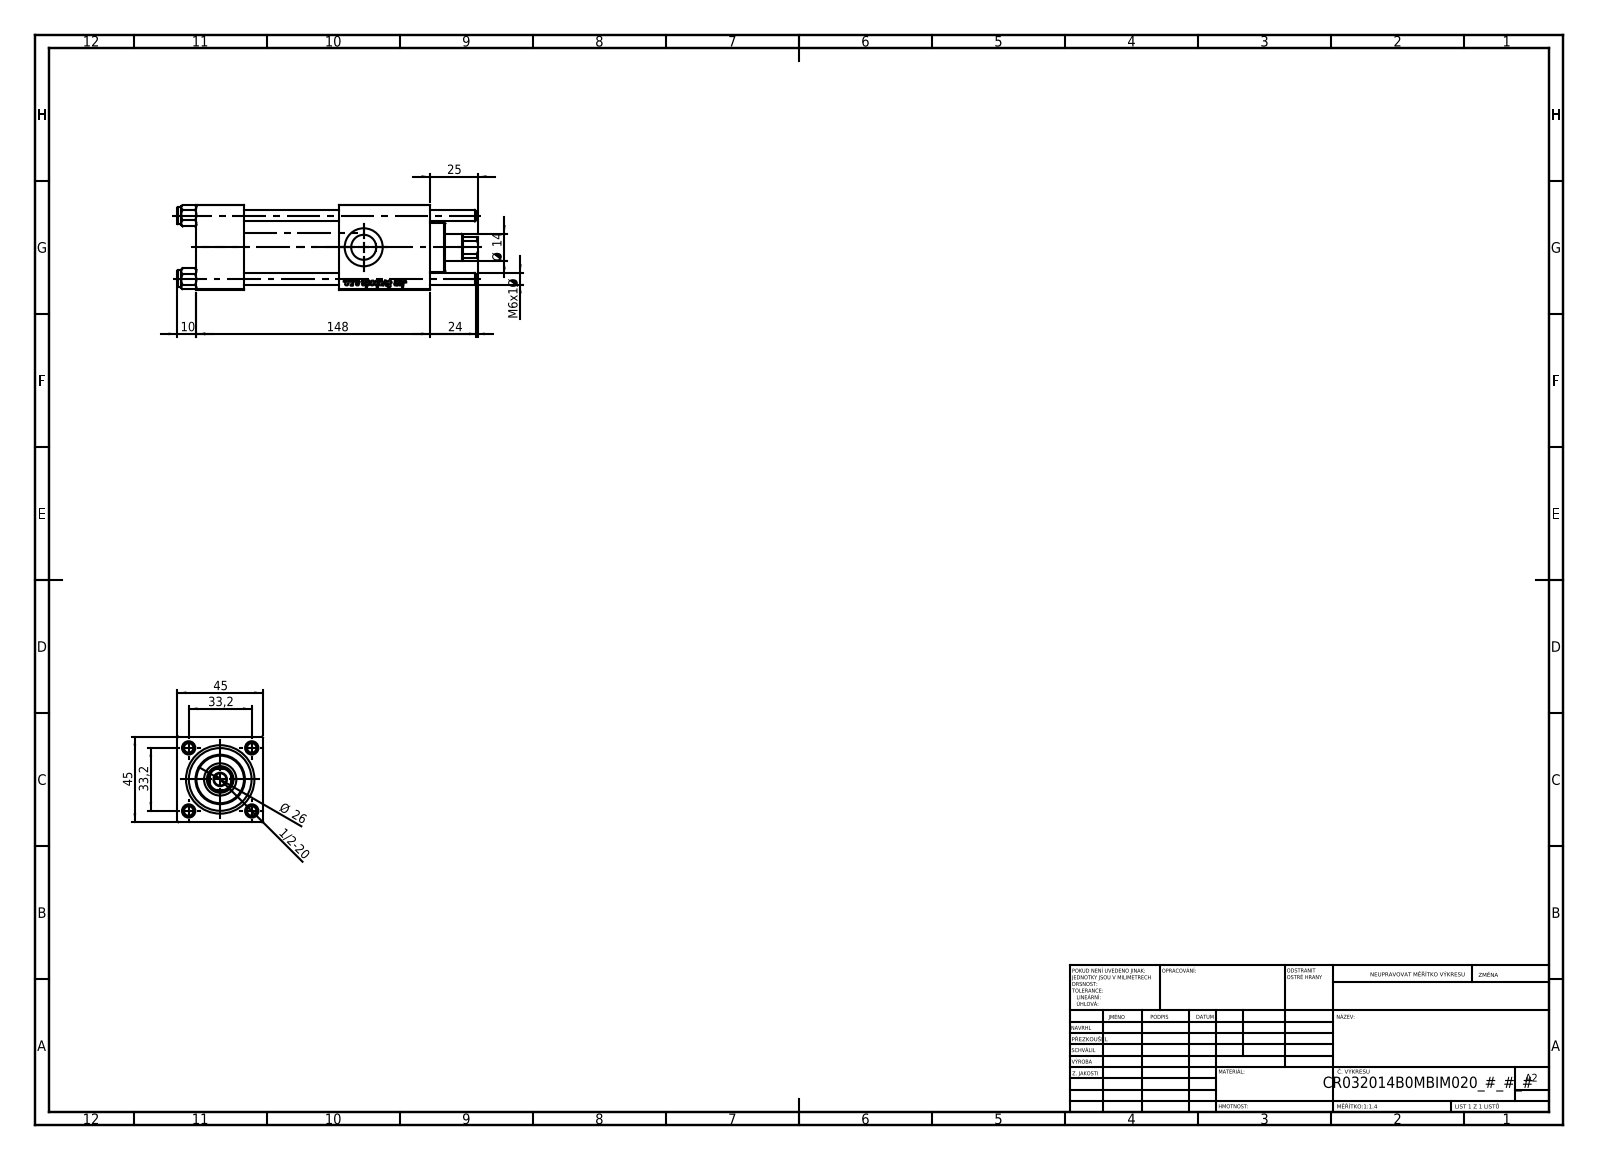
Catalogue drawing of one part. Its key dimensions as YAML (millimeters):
part_name: "V215CR_VCP_B; V215_VC_A; V215CR_B-1; V215CR_B_TYCINKA (+1 more)"
step_written_by: "SolidWorks 2019 (CONFIG_CONTROL_DESIGN)"
units: millimeters
bodies: {solids: 11, faces: 1155, planar: 429, cylindrical: 78, other: 648}
overall_size: [158, 45, 45]
volume: 198619
surface_area: 72498
round_holes:
  - {diameter: 6, count: 4}
  - {diameter: 7, count: 2}
  - {diameter: 13.16, count: 2}
  - {diameter: 20, count: 2}
  - {diameter: 6.5, count: 1}
  - {diameter: 14, count: 1}
  - {diameter: 17, count: 1}
  - {diameter: 24, count: 1}
  - {diameter: 32, count: 1}
  - {diameter: 33, count: 1}
round_bosses_or_shafts:
  - {diameter: 9, count: 4}
  - {diameter: 38, count: 1}
  - {diameter: 26, count: 1}
partial_cylinders:
  - {radius: 6.5, count: 1}
face_to_face_distances: [45, 25, 123, 98, 50, 75, 48, 94.3, 69.3, 19.3]
hole_center_spacings: [23.48, 33.2, 46.95, 75.5]
